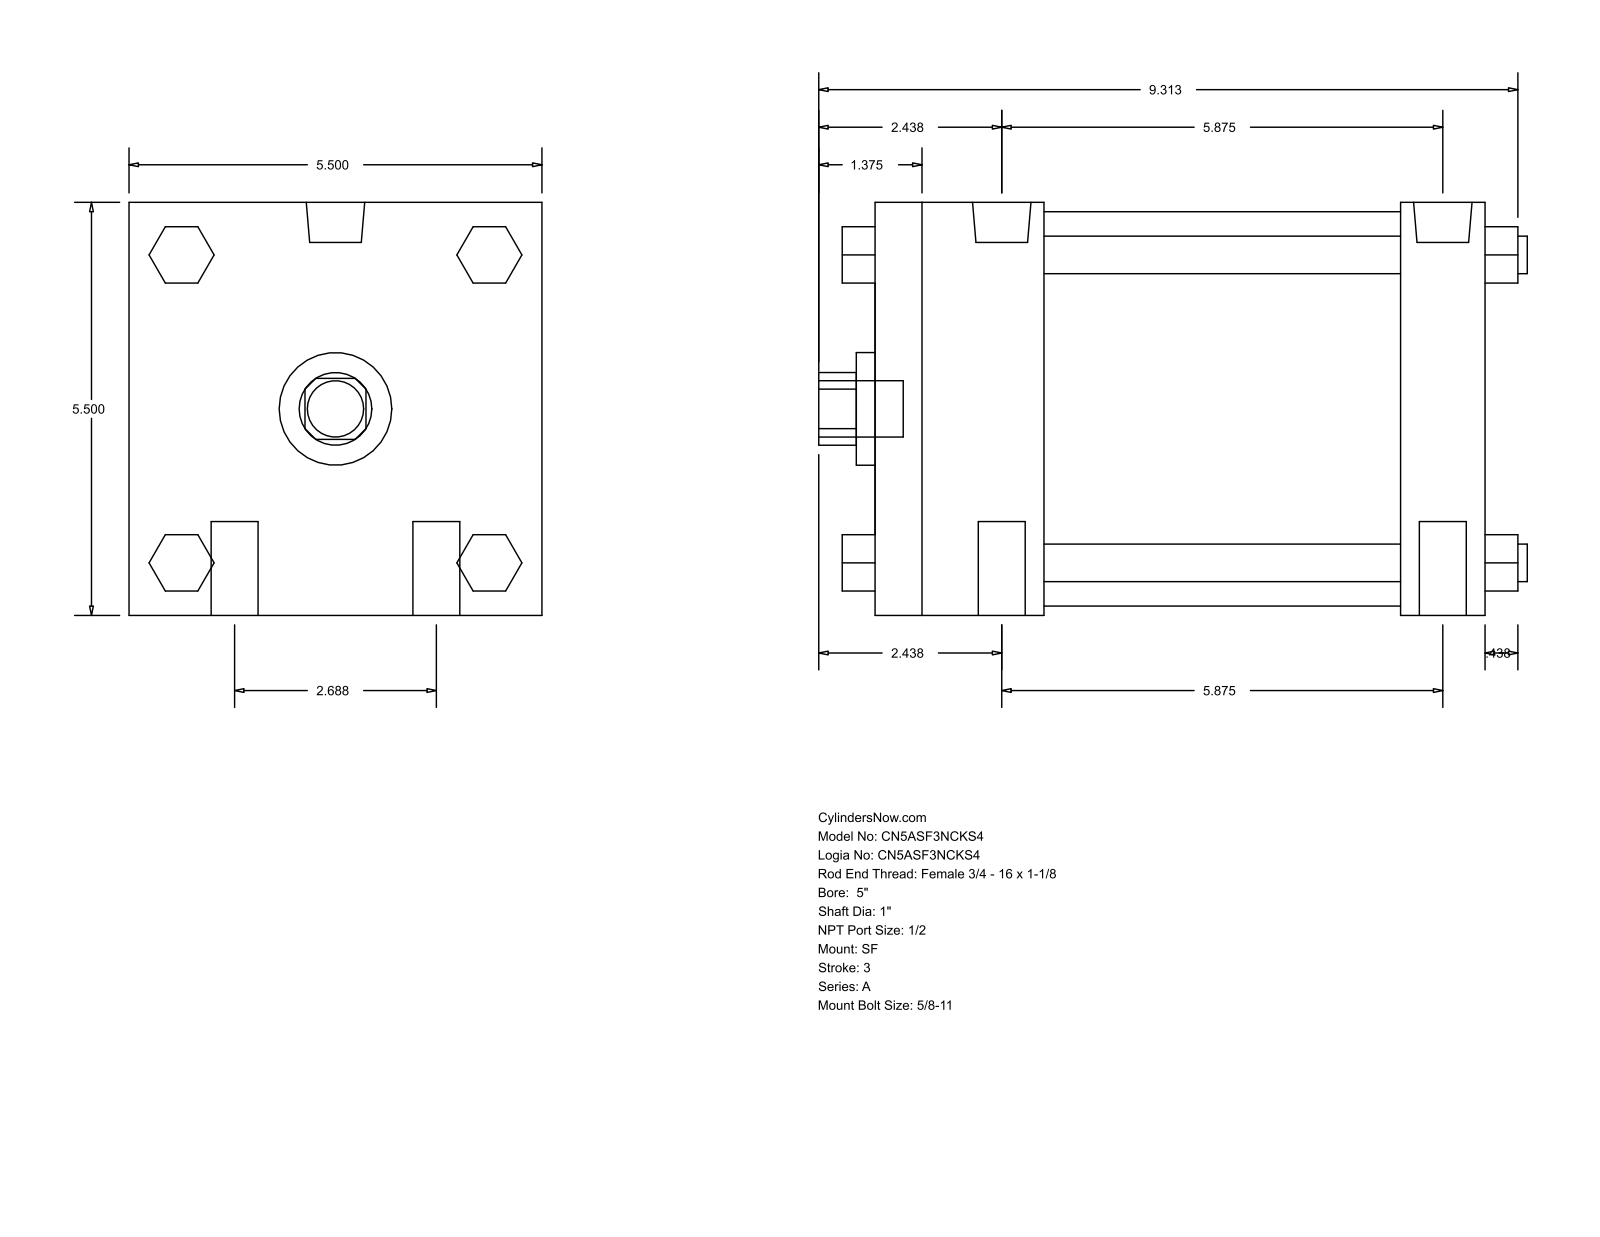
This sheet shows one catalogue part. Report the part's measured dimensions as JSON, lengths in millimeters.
{"part_name": "A_SF__0500_1", "step_written_by": "GSSL Pune (CONFIG_CONTROL_DESIGN)", "units": "millimeters", "bodies": {"solids": 0, "faces": 124, "planar": 94, "cylindrical": 30, "other": 0}, "overall_size": [239.71, 139.7, 139.7], "round_holes": [[25.4, 1], [38.1, 1], [133.35, 1]], "round_bosses_or_shafts": [[15.88, 4], [12.7, 4], [19.77, 2], [8.73, 2], [19.05, 1]], "partial_cylinders_radius": [[12.29, 1]], "face_to_face_distances": [139.7, 206.38, 57.15, 177.8, 120.65, 149.23, 28.58, 19.05, 52.07, 90.18]}
